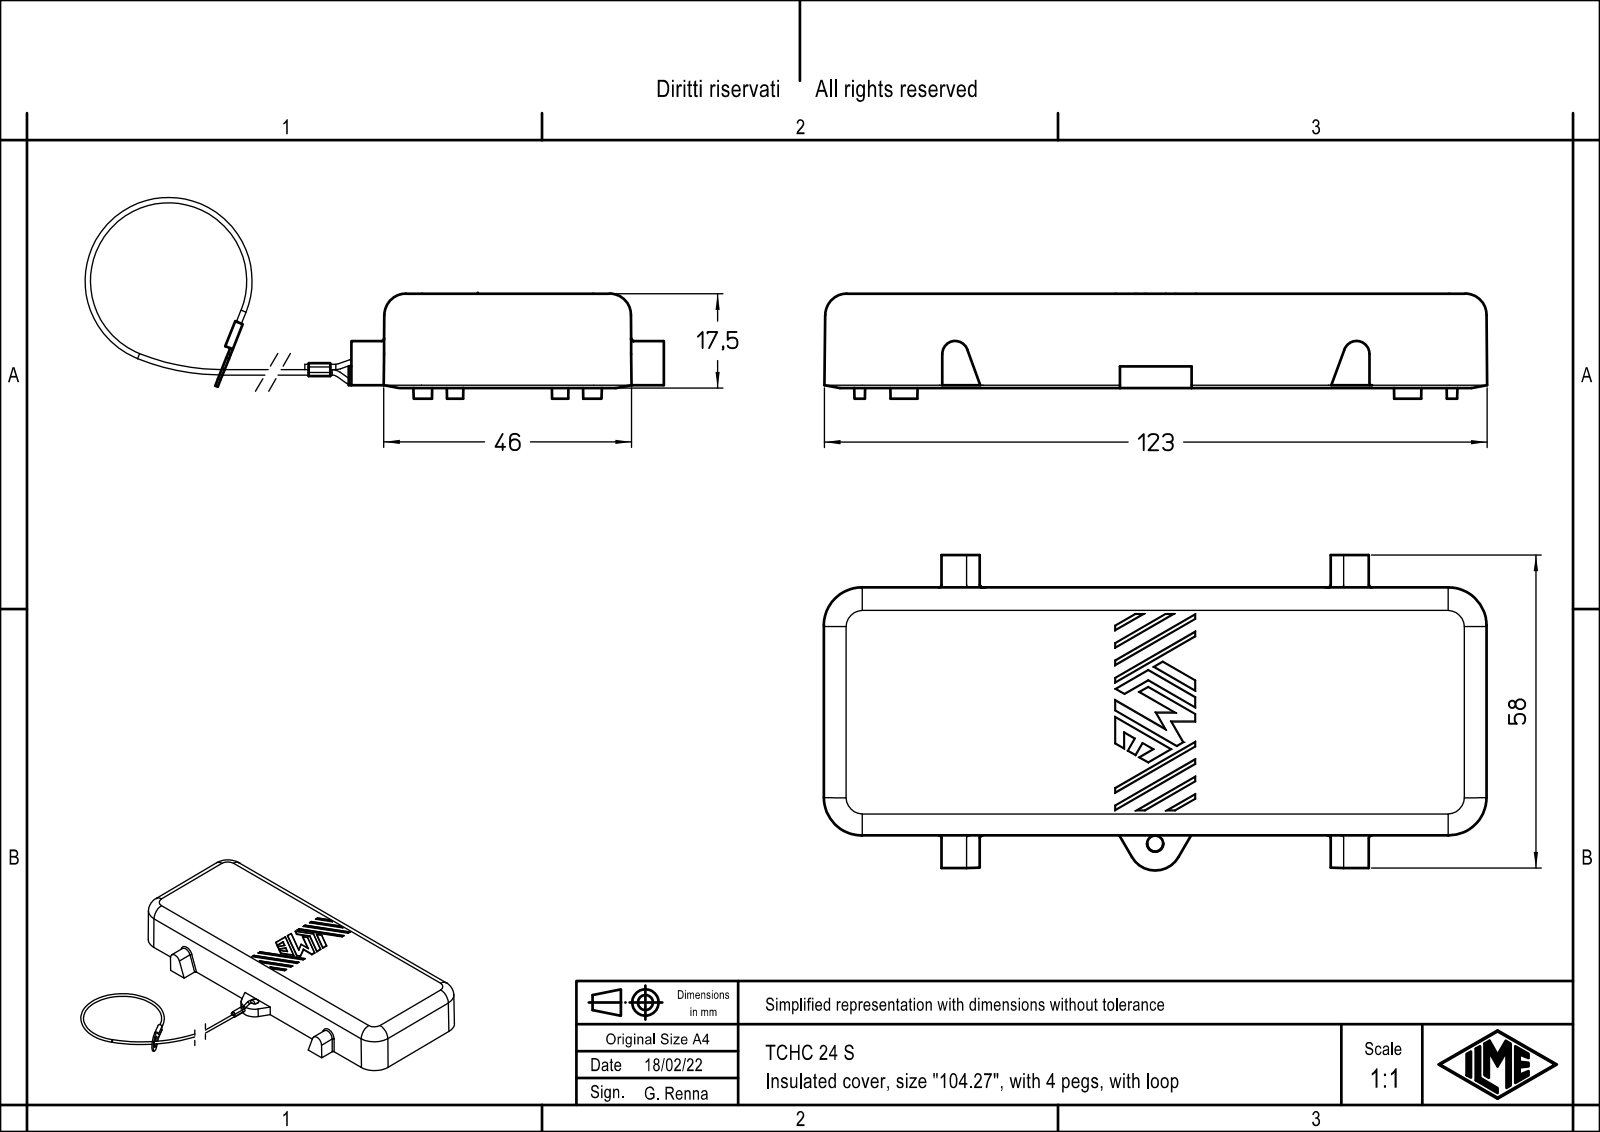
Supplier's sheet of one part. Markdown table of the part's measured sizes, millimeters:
| quantity | value |
| --- | --- |
| part name | TCHC_24_S |
| STEP written by | Creo Elements/Direct Modeling 20.1B 02-Apr-2019 (C) Parametric Technology GmbH (AUTOMOTIVE_DESIGN) |
| units | millimeters |
| bodies | 1 solid, 282 faces (120 planar, 114 cylindrical, 48 other) |
| overall size | 228.27 × 122.99 × 19.65 |
| volume | 52 155 mm³ |
| surface area | 22 039 mm² |
| round holes (diameter × count) | 3 × 1, 4.2 × 1 |
| round bosses / shafts (diameter × count) | 1 × 5, 7 × 1 |
| partial cylindrical surfaces (radius × count) | 0.15 × 44, 1.5 × 4, 4 × 4, 7 × 4, 0.7 × 2, 0.75 × 2, 1.25 × 2, 2.4 × 2 |
| main face-to-face distances | 5.5, 7, 6.99, 5.65, 11.49, 16.99, 17.14, 76.58, 19.5, 58 |
